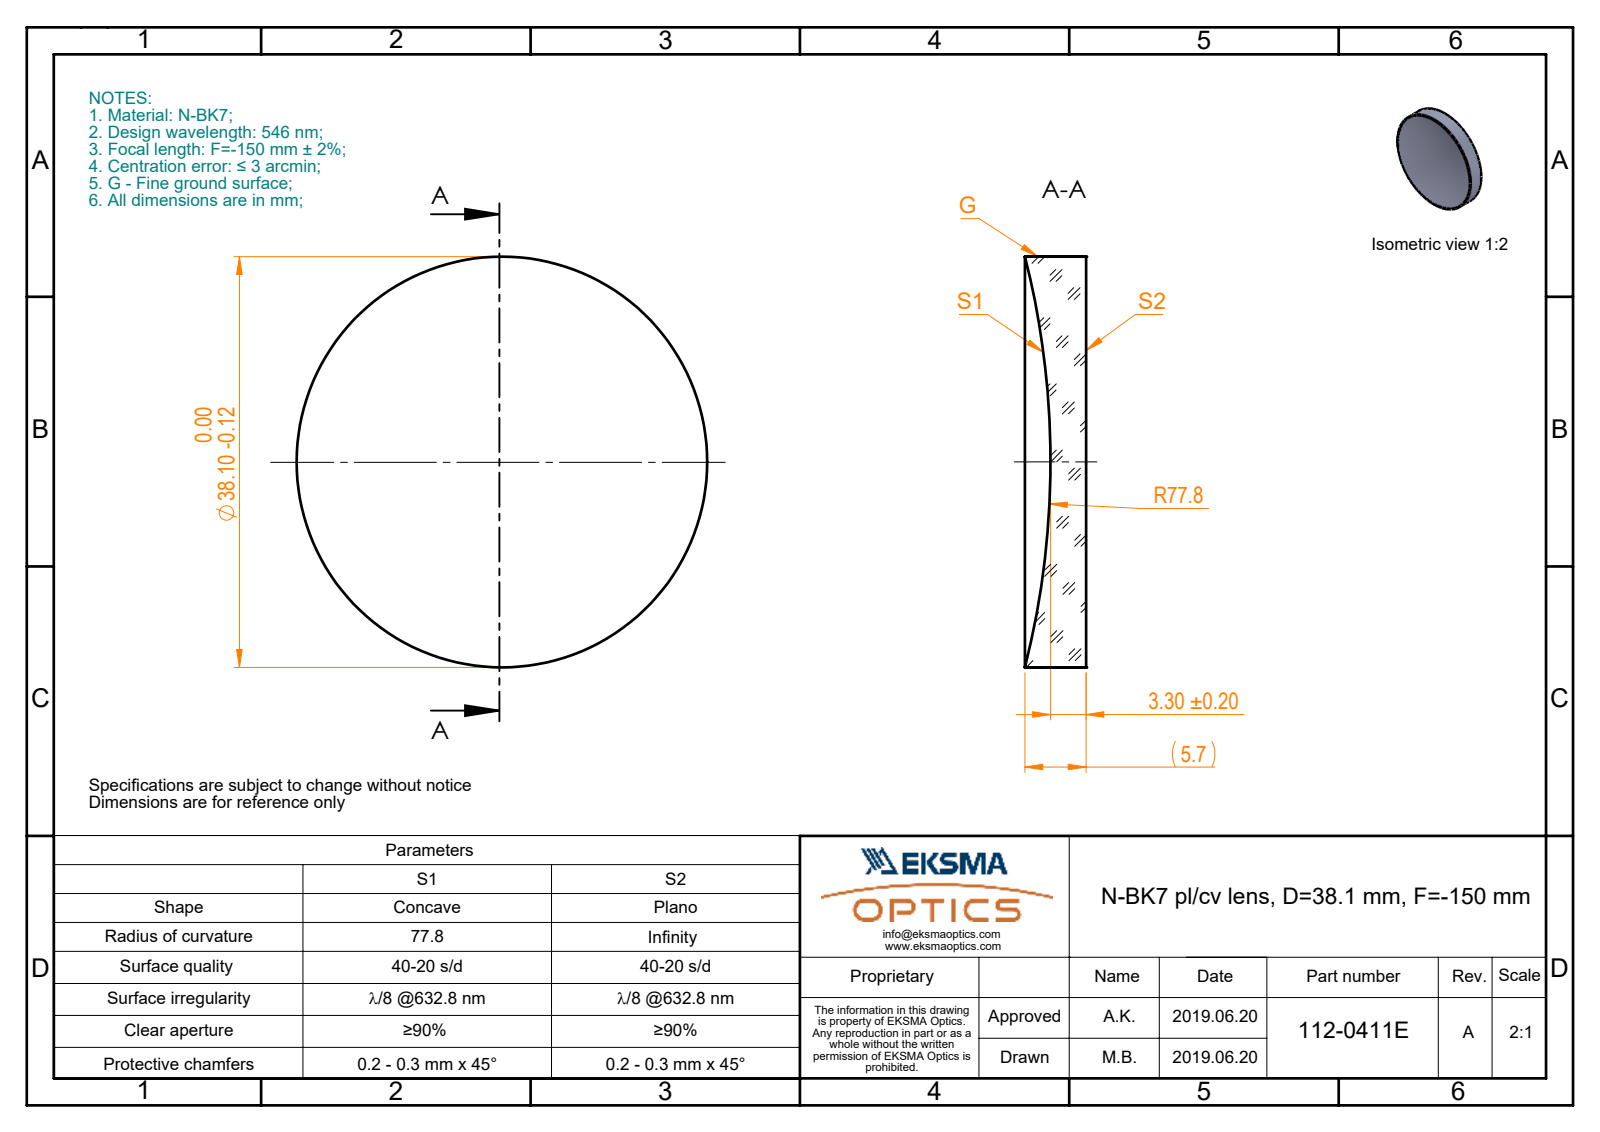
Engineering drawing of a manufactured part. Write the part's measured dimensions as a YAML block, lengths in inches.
part_name: "112-0411E BK7 pl-cv 38.1 F-150"
step_written_by: "SolidWorks 2017 (CONFIG_CONTROL_DESIGN)"
units: inches
bodies: {solids: 1, faces: 5, planar: 1, cylindrical: 2, other: 2}
overall_size: [1.5, 1.5, 0.223]
volume: 0.312
surface_area: 4.613
round_bosses_or_shafts:
  - {diameter: 1.5, count: 1}
